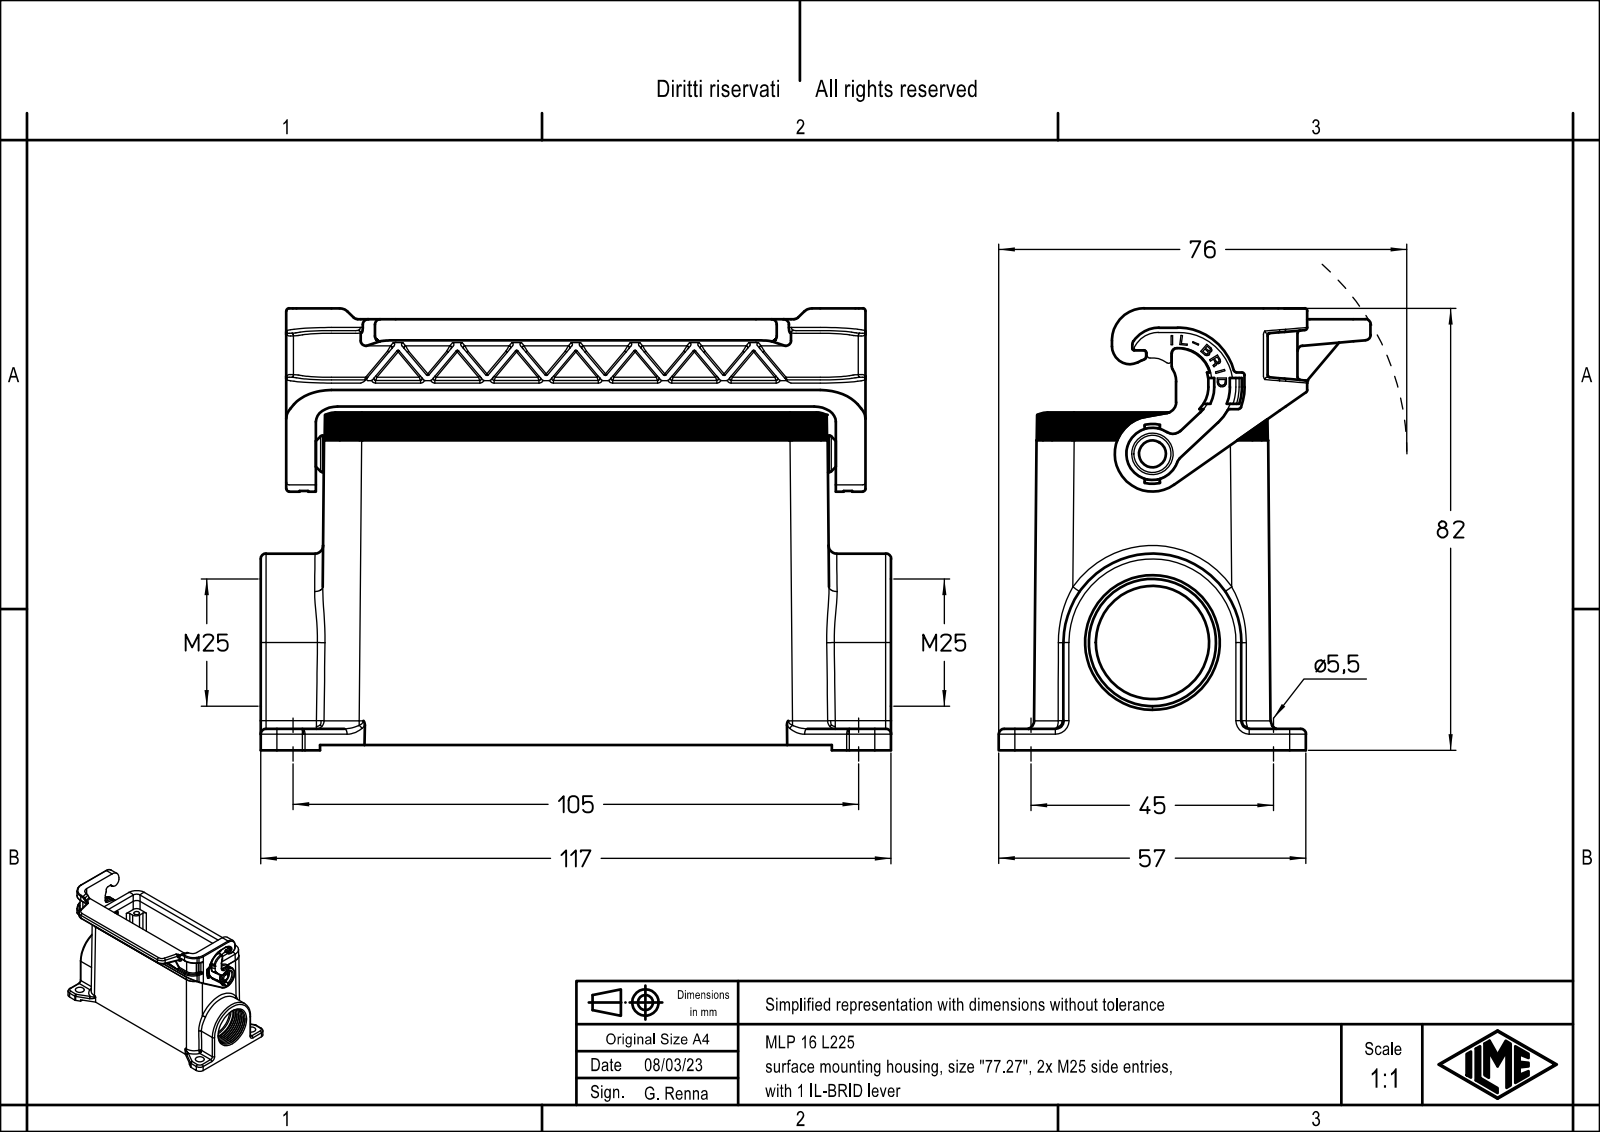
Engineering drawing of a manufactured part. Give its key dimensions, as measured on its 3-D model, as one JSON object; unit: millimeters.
{"part_name": "MLP 16 L225", "step_written_by": "Creo Elements/Direct Modeling 20.1B 02-Apr-2019 (C) Parametric Technology GmbH (AUTOMOTIVE_DESIGN)", "units": "millimeters", "bodies": {"solids": 1, "faces": 1108, "planar": 637, "cylindrical": 295, "other": 176}, "overall_size": [117, 82, 69], "volume_mm3": 110868, "surface_area_mm2": 60268, "round_holes": [[3, 4], [3.5, 4], [5.5, 4], [3.25, 1], [5.4, 1], [7.7, 1], [21, 1], [23.6, 1]], "round_bosses_or_shafts": [[6.9, 1], [6.8, 1], [5.2, 1], [3.2, 1]], "partial_cylinders_radius": [[0.1, 27], [1, 19], [3, 16], [0.2, 15], [1.5, 13], [0.5, 11], [7, 10], [2, 9]], "face_to_face_distances": [3, 10.25, 106.75, 1, 79, 76, 4, 4.75, 5.5, 112.25], "hole_center_spacings": [16.43, 38.54, 91.69, 98.09, 27, 45, 77.5, 82.07]}
